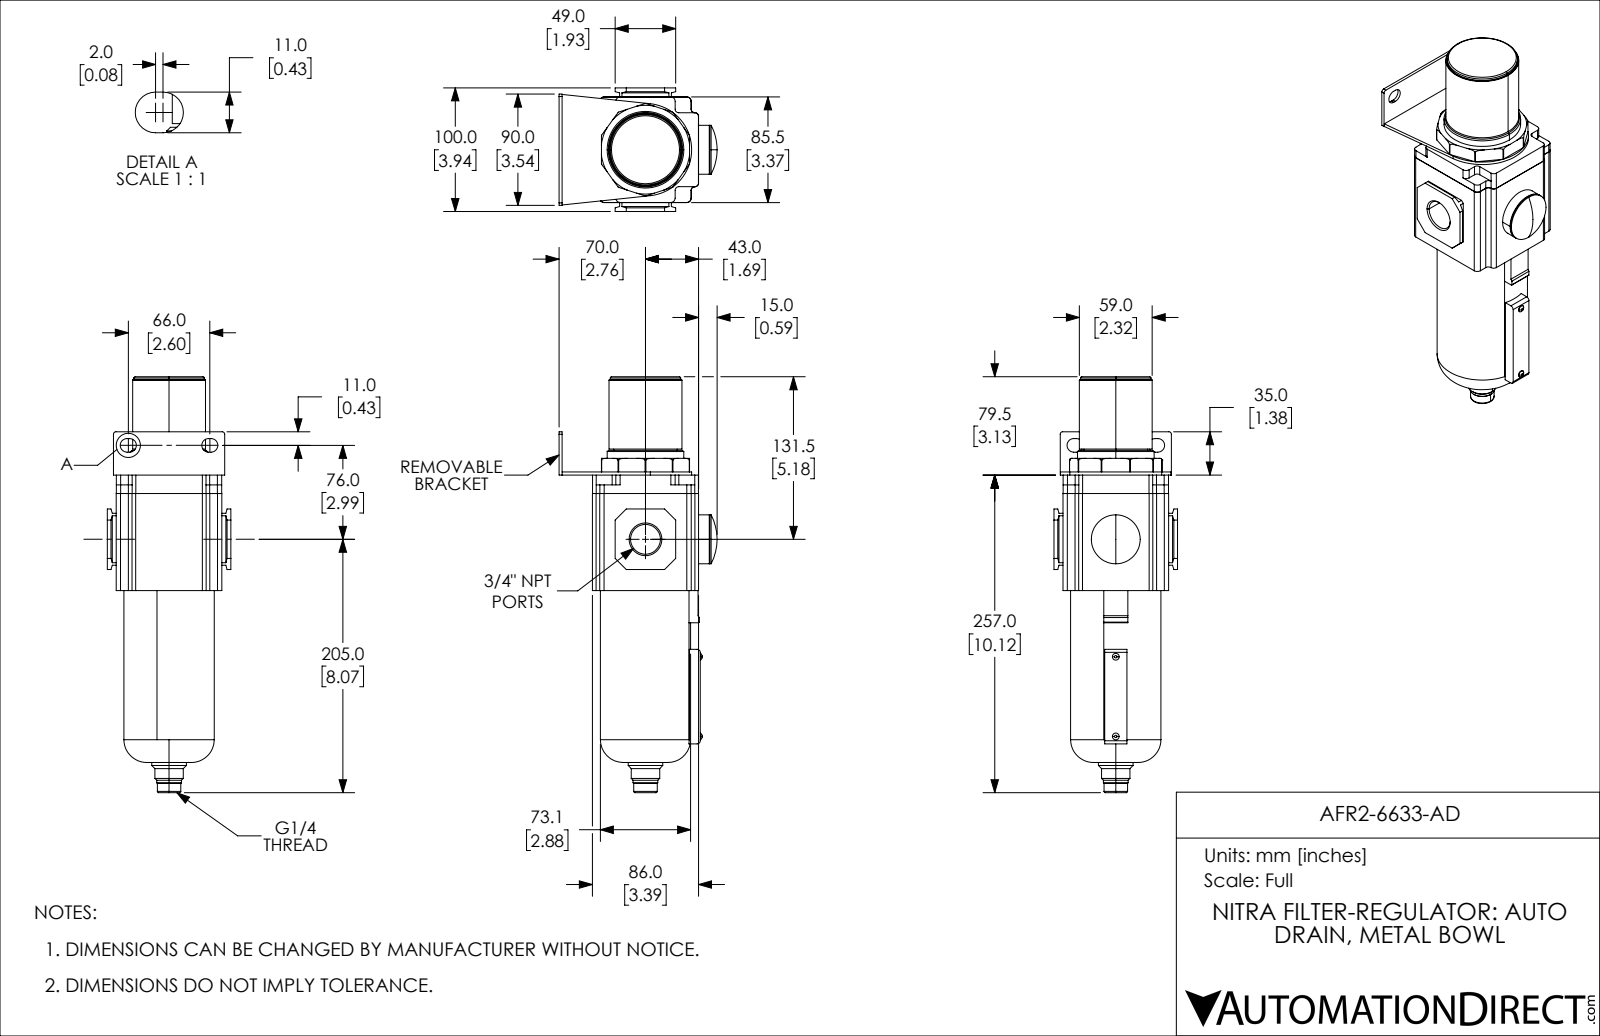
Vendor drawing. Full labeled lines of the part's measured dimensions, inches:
Part name (STEP PRODUCT): AFR2-6633-AD
STEP written by: SolidWorks 2019 (CONFIG_CONTROL_DESIGN)
Units: inches
Bodies: 1 solid, 235 faces (116 planar, 79 cylindrical, 40 other)
Overall size (bounding box): 13.248 × 5.039 × 3.937
Volume: 92.63 in³ · Surface area: 179.5 in²
Round holes (diameter × count): ⌀0.451 ×1, ⌀0.95 ×1
Round bosses / shafts (diameter × count): ⌀0.217 ×2, ⌀2.878 ×1, ⌀2.441 ×1, ⌀2.323 ×1, ⌀2.244 ×1, ⌀2.024 ×1, ⌀1.559 ×1, ⌀1.102 ×1
Partial cylindrical surfaces — rounded edges, fillets, slot ends (radius × count): R0.118 ×20, R0.138 ×12, R0.217 ×4, R0.079 ×2, R0.098 ×2, R1.472 ×1
Main face-to-face distances: 0.098, 3.366, 0.285, 3.652, 3.386, 4.35, 1.063, 4.449, 3.681, 3.78
